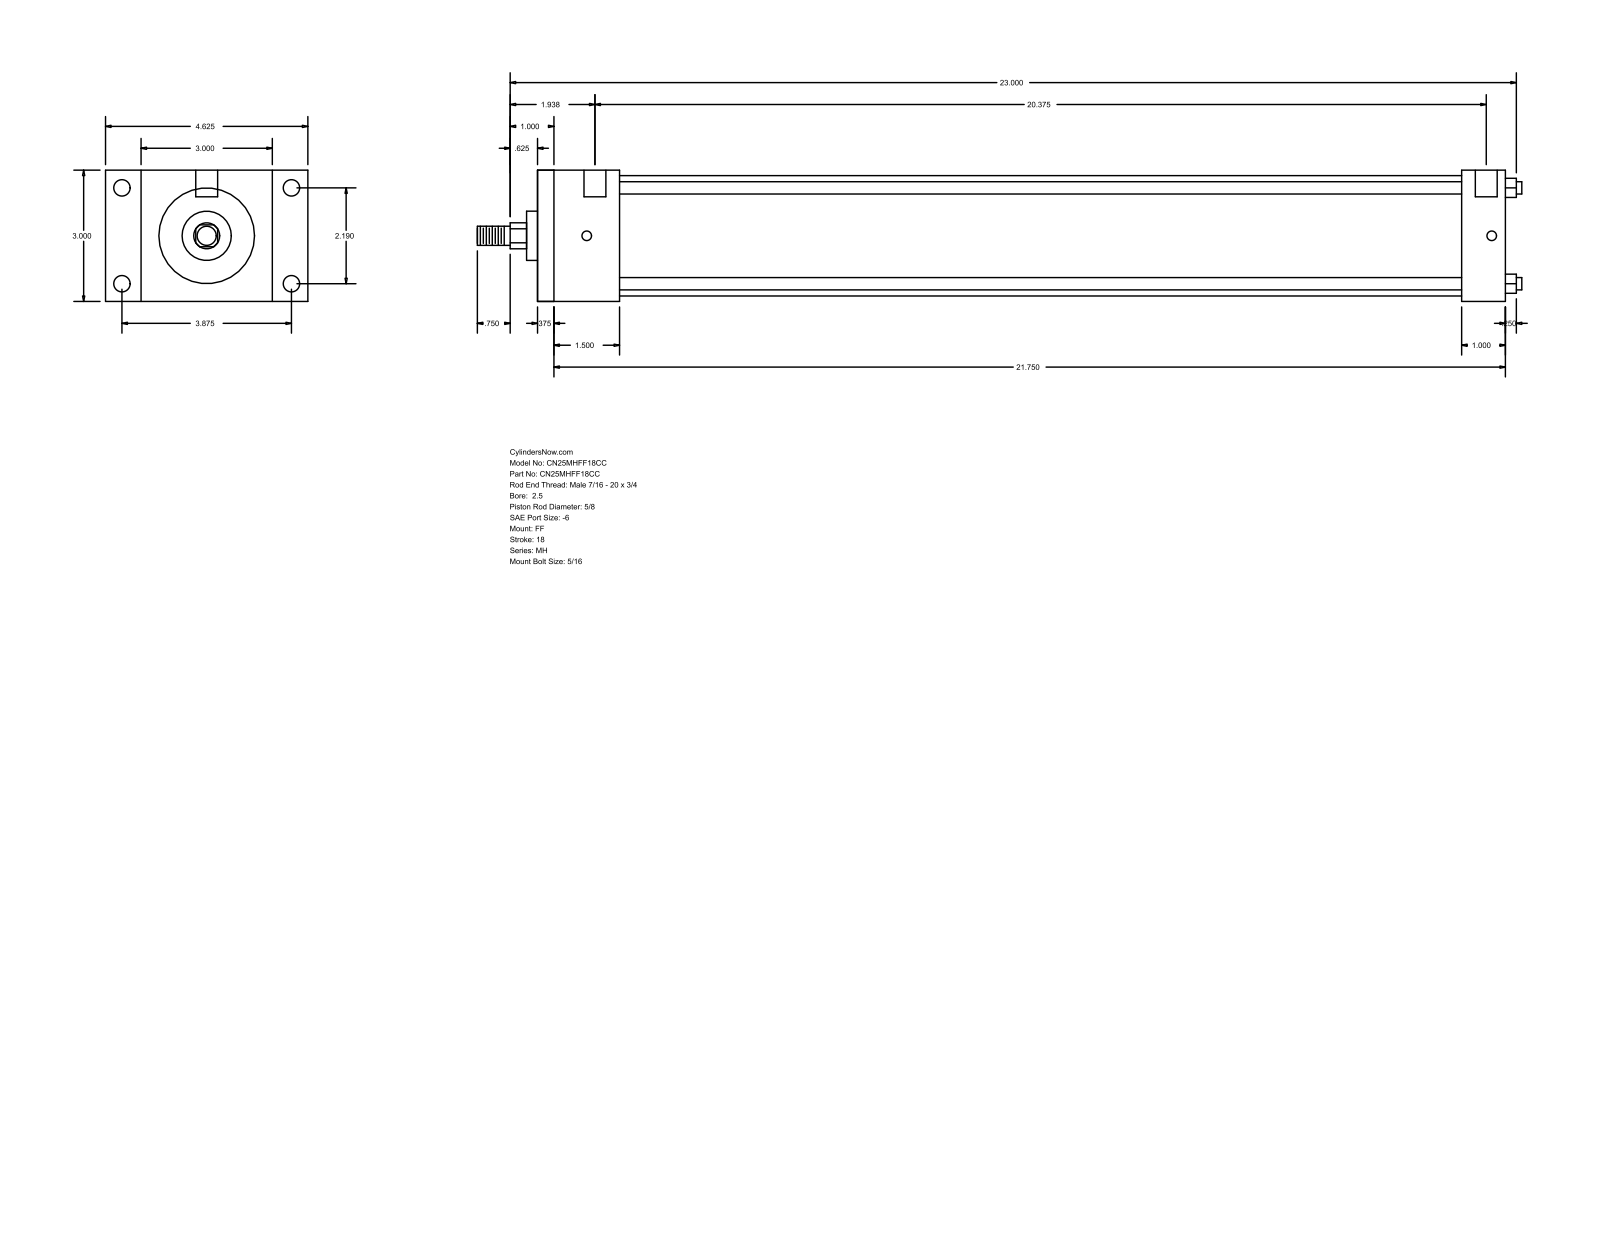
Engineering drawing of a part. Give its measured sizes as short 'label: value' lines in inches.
name: MH_FF__0250_0.625
written by: GSSL Pune (CONFIG_CONTROL_DESIGN)
unit: in
bodies: 0 solids, 92 faces (64 planar, 28 cylindrical, 0 other)
size: 23.875 × 4.625 × 3
holes: 4× ⌀0.219, 4× ⌀0.375, 2× ⌀0.5
bosses: 4× ⌀0.281, 1× ⌀2.75, 1× ⌀1.125, 1× ⌀0.625, 1× ⌀0.437
rounds: 1× R0.297
face distances: 3, 22.125, 21.75, 0.375, 1, 1.875, 21.125, 1.5, 20.75, 19.25
hole spacings: 2.19, 3.875, 4.451, 20.687, 0.125, 0.187, 20.375, 20.5
